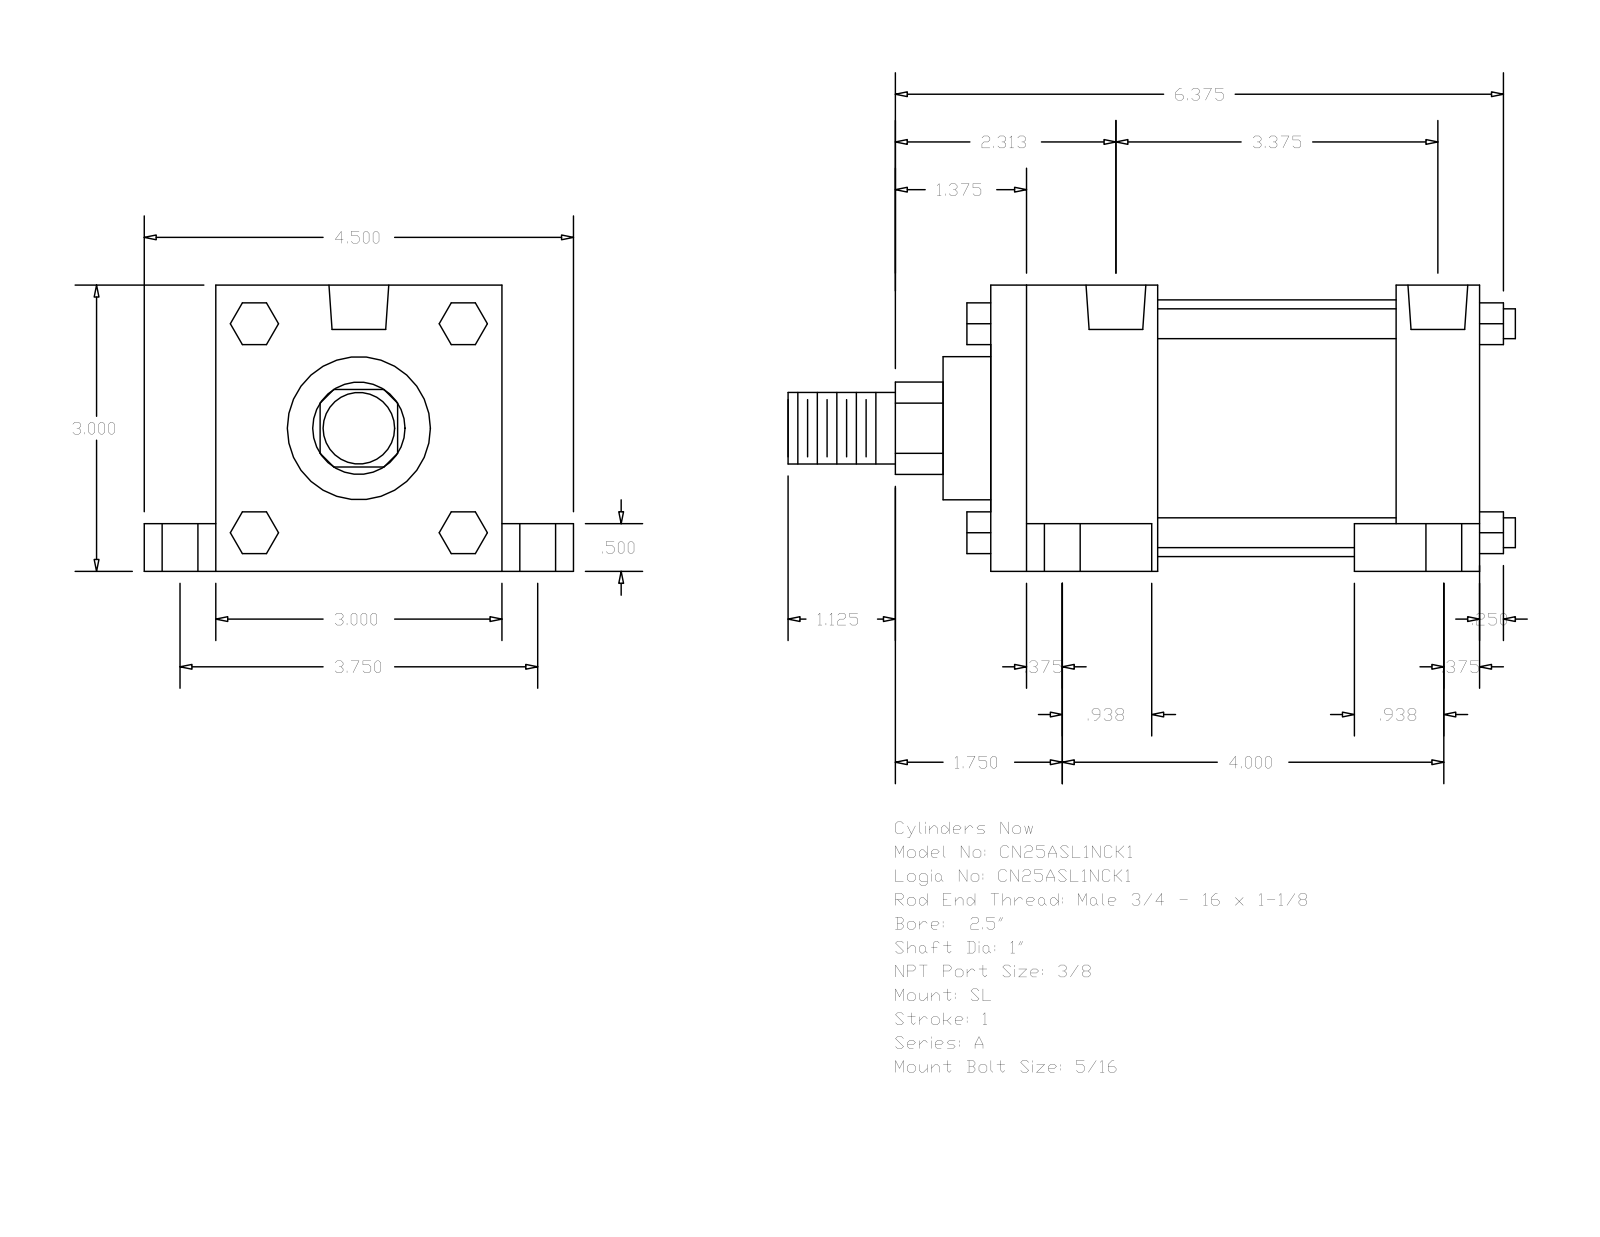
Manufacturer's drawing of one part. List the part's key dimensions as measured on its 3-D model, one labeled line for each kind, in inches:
Part name (STEP PRODUCT): A_SL__0250_1
STEP written by: GSSL Pune (CONFIG_CONTROL_DESIGN)
Units: inches
Bodies: 0 solids, 148 faces (112 planar, 36 cylindrical, 0 other)
Overall size (bounding box): 7.625 × 4.5 × 3
Round holes (diameter × count): ⌀0.219 ×4, ⌀0.375 ×4, ⌀0.625 ×4, ⌀0.627 ×2
Round bosses / shafts (diameter × count): ⌀0.313 ×4, ⌀2.69 ×1, ⌀1.5 ×1, ⌀1 ×1, ⌀0.75 ×1
Partial cylindrical surfaces — rounded edges, fillets, slot ends (radius × count): R0.484 ×1
Main face-to-face distances: 3, 5.125, 2.5, 0.5, 0.875, 1.75, 3.375, 4.25, 3.75, 0.75
Hole centre spacings: 0.094, 1.875, 1.876, 1.933, 1.957, 3.469, 3.562, 3.75
